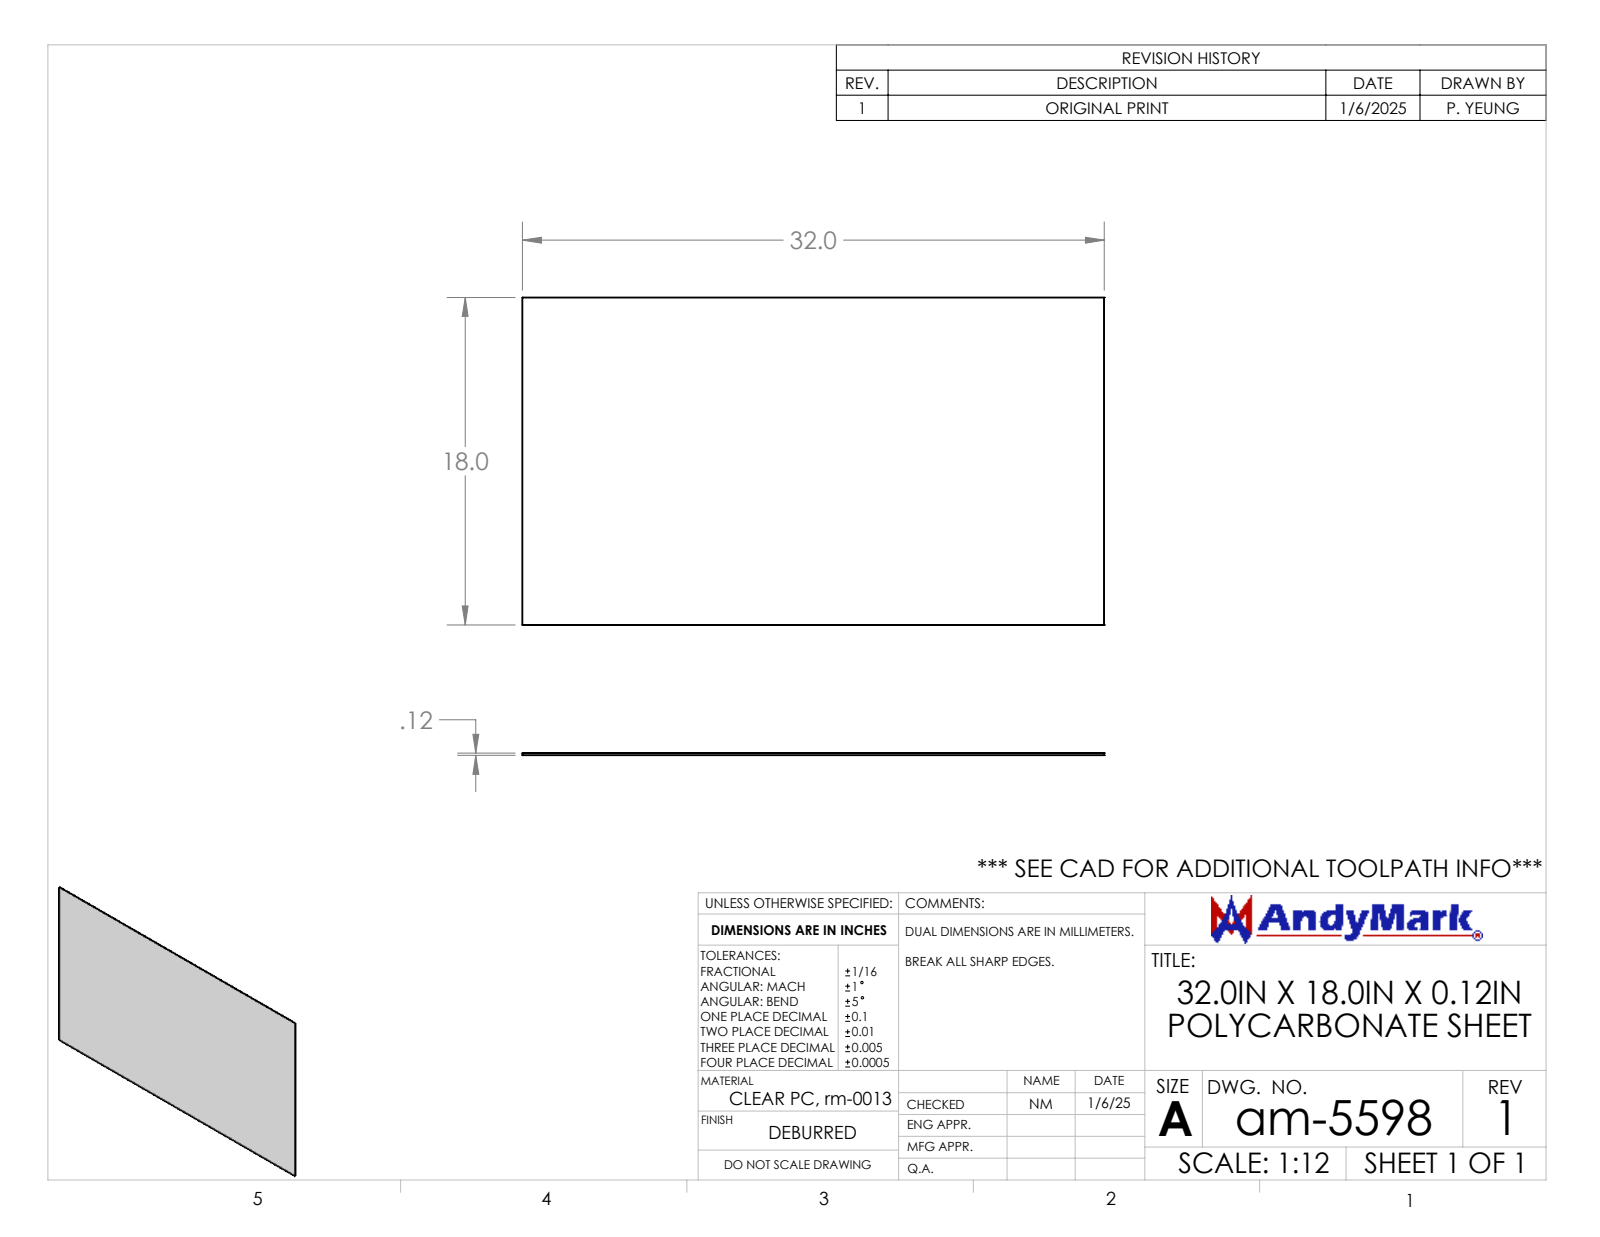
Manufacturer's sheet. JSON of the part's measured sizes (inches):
{"part_name": "am-5598 32x18x.125 Polycarbonate Sheet", "step_written_by": "SolidWorks 2024 (AUTOMOTIVE_DESIGN)", "units": "inches", "bodies": {"solids": 1, "faces": 6, "planar": 6, "cylindrical": 0, "other": 0}, "overall_size": [32, 18, 0.118], "volume_in3": 67.97, "surface_area_in2": 1164, "face_to_face_distances": [0.118, 18, 32]}
